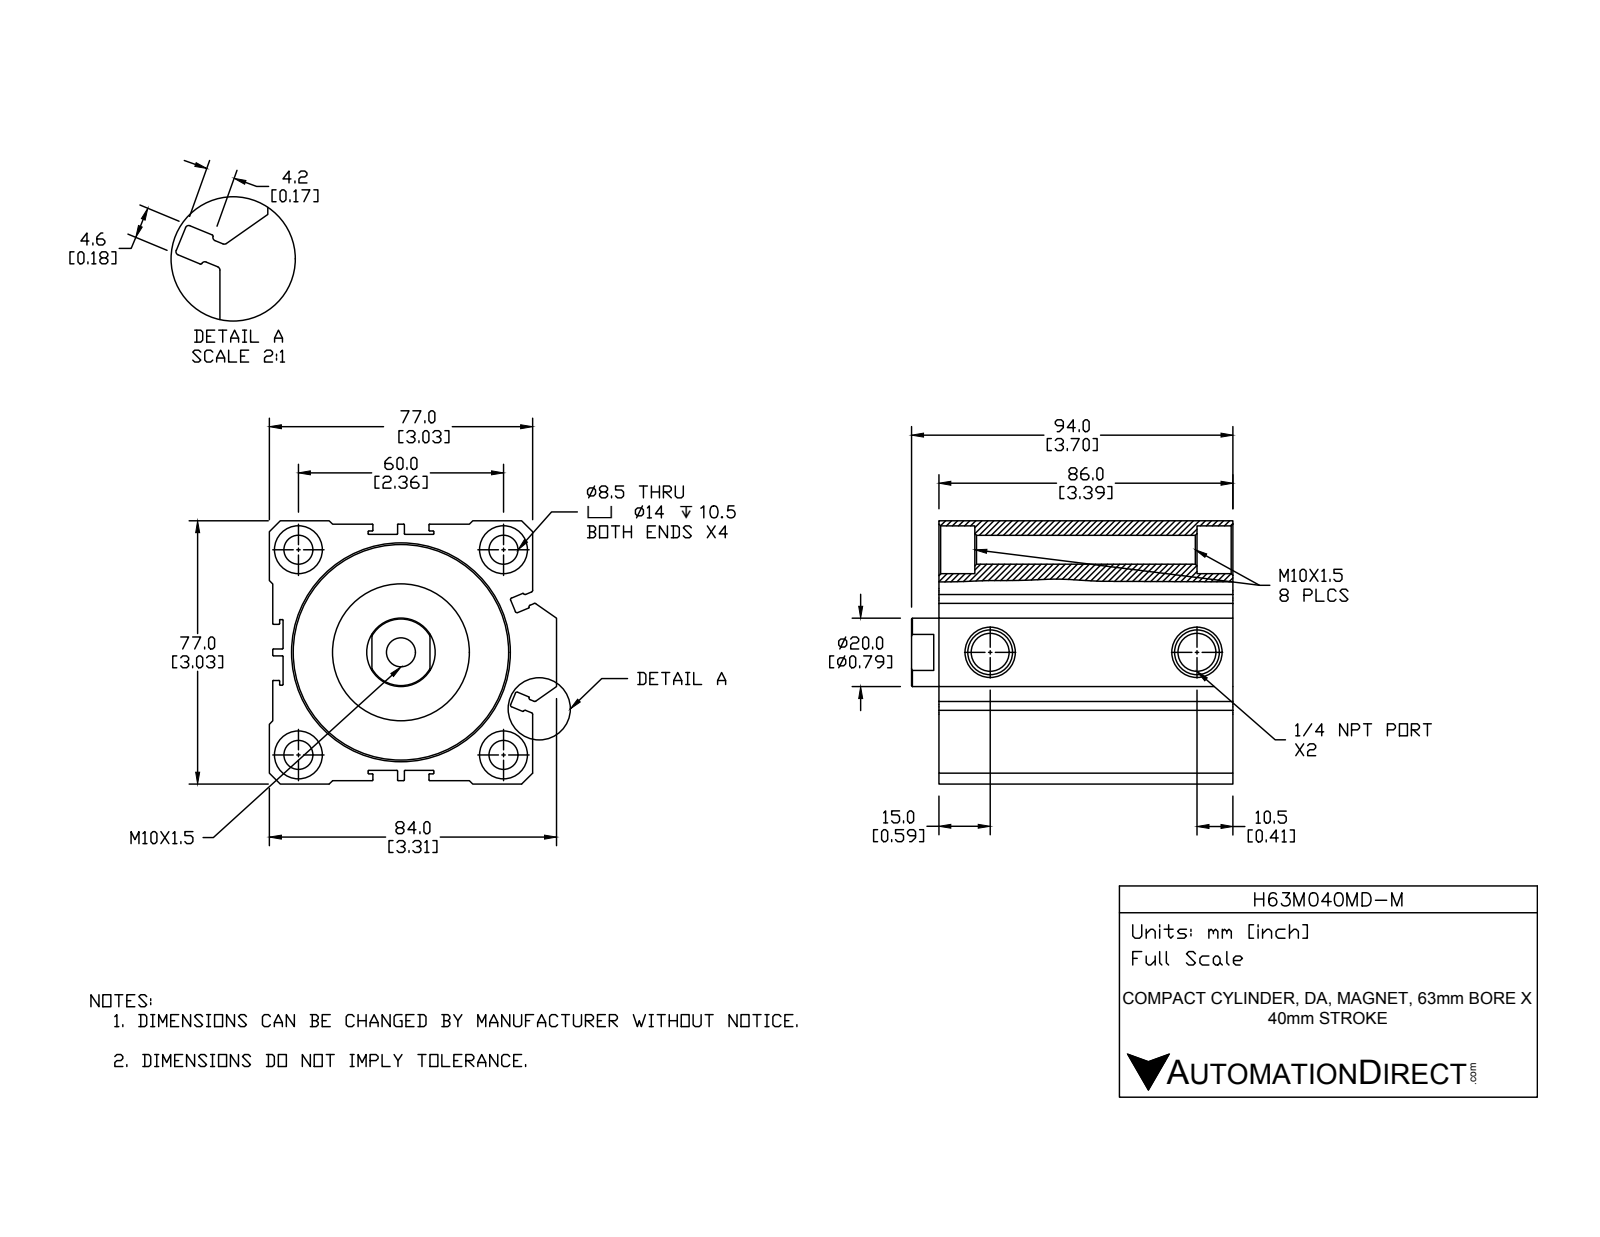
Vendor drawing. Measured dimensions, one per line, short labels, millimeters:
name: H63M040MD-M-BODY; H63M040MD-M; H63M040MD-M-PISTON
written by: SolidWorks 2015 (CONFIG_CONTROL_DESIGN)
unit: mm
bodies: 2 solids, 255 faces (99 planar, 103 cylindrical, 53 other)
size: 94 × 84 × 77
volume: 335 945 mm³; area: 92 325 mm²
holes: 5× ⌀8.5, 4× ⌀14, 2× ⌀11.13, 1× ⌀20, 1× ⌀45.51, 1× ⌀63
bosses: 1× ⌀40, 1× ⌀39
rounds: 40× R0.2, 12× R0.5
face distances: 1, 76, 3, 77, 4, 73, 69, 84, 2, 23
hole spacings: 42.43, 60, 84.85, 60.5
